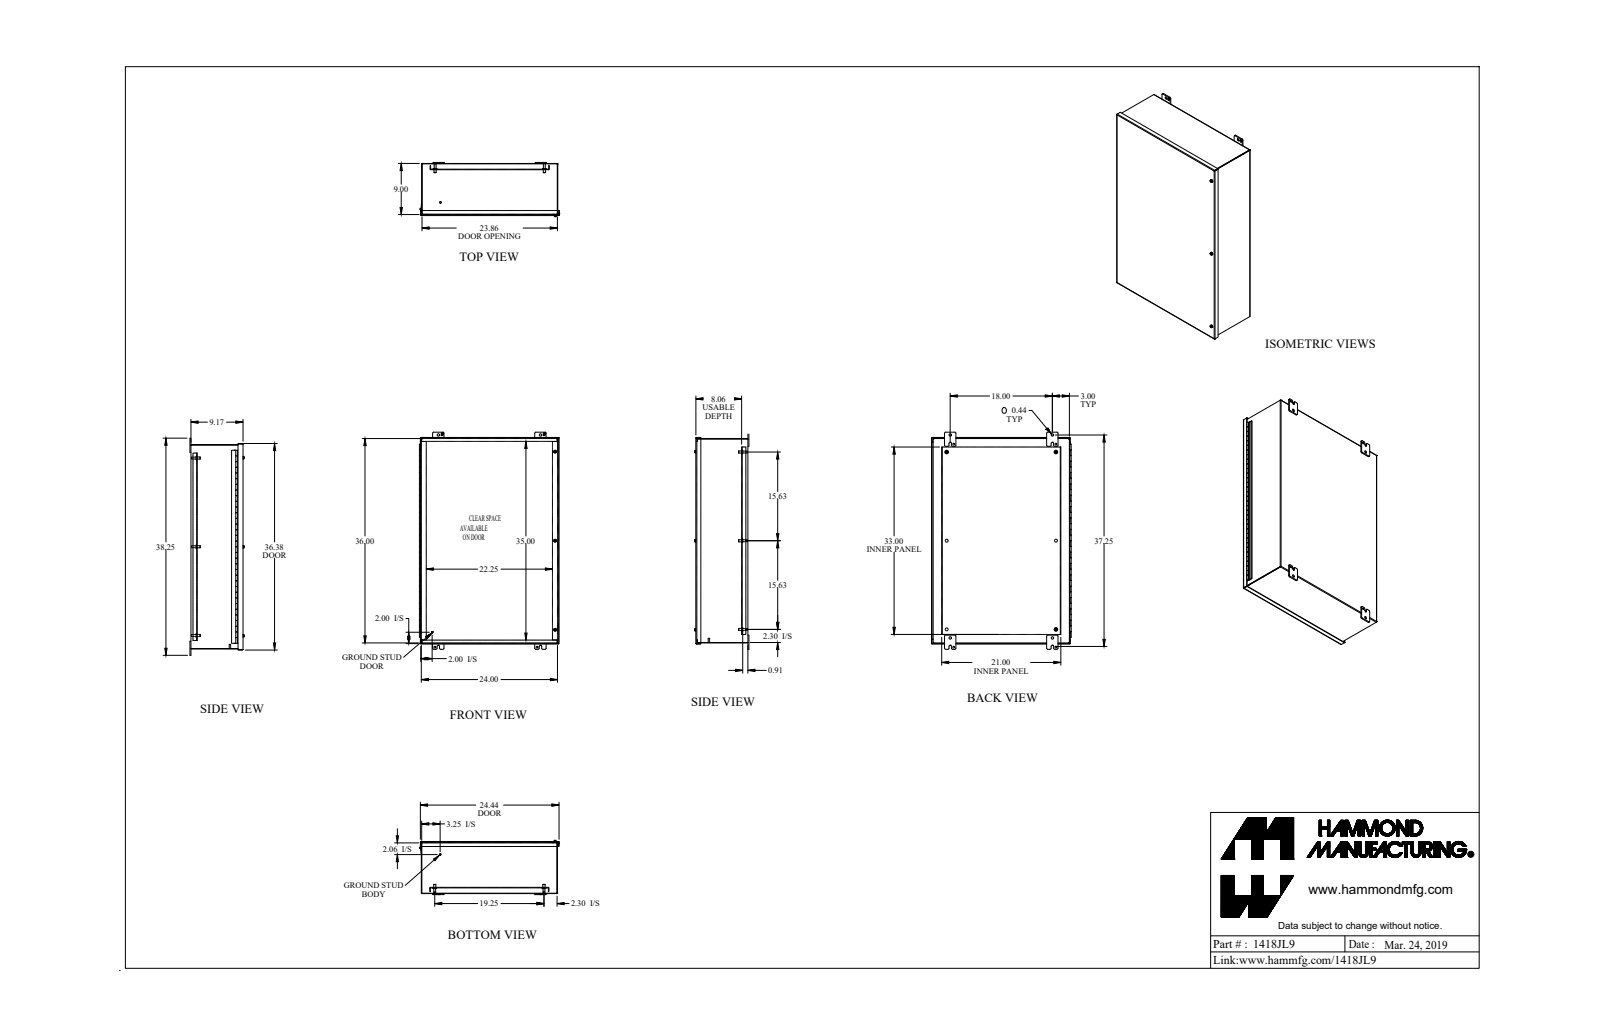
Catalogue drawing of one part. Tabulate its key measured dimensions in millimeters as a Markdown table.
| quantity | value |
| --- | --- |
| part name | 1418JL9_Default |
| STEP written by | SolidWorks 2018 (CONFIG_CONTROL_DESIGN) |
| units | millimeters |
| bodies | 42 solids, 1161 faces (684 planar, 415 cylindrical, 62 other) |
| overall size | 971.6 × 624.9 × 243.1 |
| volume | 5 349 000 mm³ |
| surface area | 5 235 000 mm² |
| round holes (diameter × count) | 8 × 7, 12.7 × 6, 7.8 × 4, 11.1 × 4, 6.6 × 3, 6.8 × 3, 7.1 × 3, 7.4 × 3, 10.1 × 3, 11.3 × 2, 11.3 × 2, 4.7 × 1 |
| round bosses / shafts (diameter × count) | 16.5 × 6, 9.5 × 6, 8.4 × 6, 25.4 × 4, 13 × 3, 12.7 × 3, 9.9 × 3, 6.2 × 3 |
| partial cylindrical surfaces (radius × count) | 4.8 × 24, 6.4 × 20, 0.9 × 12, 2.7 × 12, 5.5 × 8, 3.4 × 6, 1.5 × 5, 3.2 × 5 |
| main face-to-face distances | 1.8, 231.1, 233, 229.3, 2.4, 203.1, 28, 26.2, 204.9, 205.5 |
| hole center spacings | 396.9, 489, 793.8, 932.3, 960.7, 398.4, 398.4, 457.2 |
